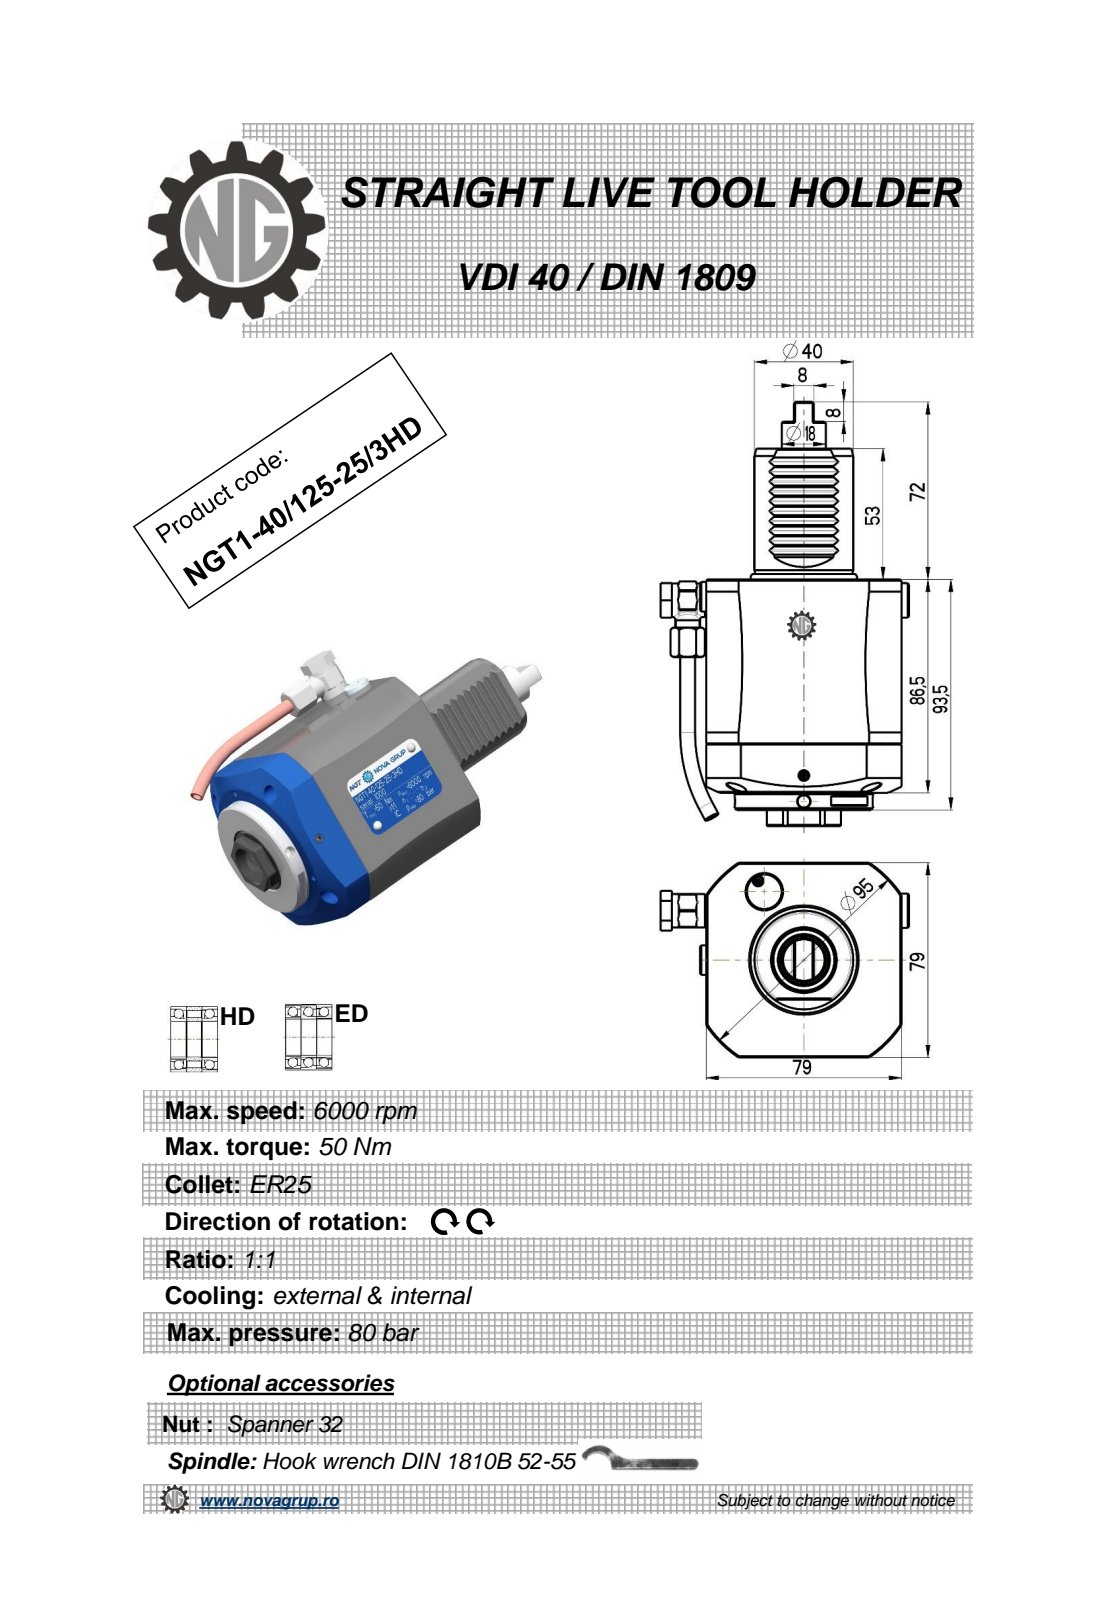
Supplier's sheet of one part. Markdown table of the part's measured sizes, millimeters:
| quantity | value |
| --- | --- |
| part name | NGT1_40_125_25_3HD |
| STEP written by | PRO/ENGINEER BY PARAMETRIC TECHNOLOGY CORPORATION, 2010280 (CONFIG_CONTROL_DESIGN) |
| units | millimeters |
| bodies | 2 solids, 379 faces (153 planar, 107 cylindrical, 119 other) |
| overall size | 172 × 100.4 × 79 |
| volume | 593 122 mm³ |
| surface area | 52 627 mm² |
| round holes (diameter × count) | 4 × 3, 5 × 2, 3 × 1, 6 × 1, 6.2 × 1, 9 × 1, 10 × 1, 11 × 1, 18 × 1, 26.5 × 1 |
| round bosses / shafts (diameter × count) | 56 × 1, 40 × 1, 17.8 × 1, 14 × 1, 13.6 × 1, 13 × 1, 12 × 1, 10 × 1 |
| partial cylindrical surfaces (radius × count) | 0.3 × 10, 0.41 × 6, 0.5 × 4, 0.8 × 2, 7.7 × 1, 15 × 1, 47 × 1, 47.5 × 1 |
| main face-to-face distances | 79, 86.5, 7, 93.5, 53, 146.5, 139.5, 2.83, 8.48, 14.14 |
| hole center spacings | 0.4, 51.08, 51.45, 83.92 |
